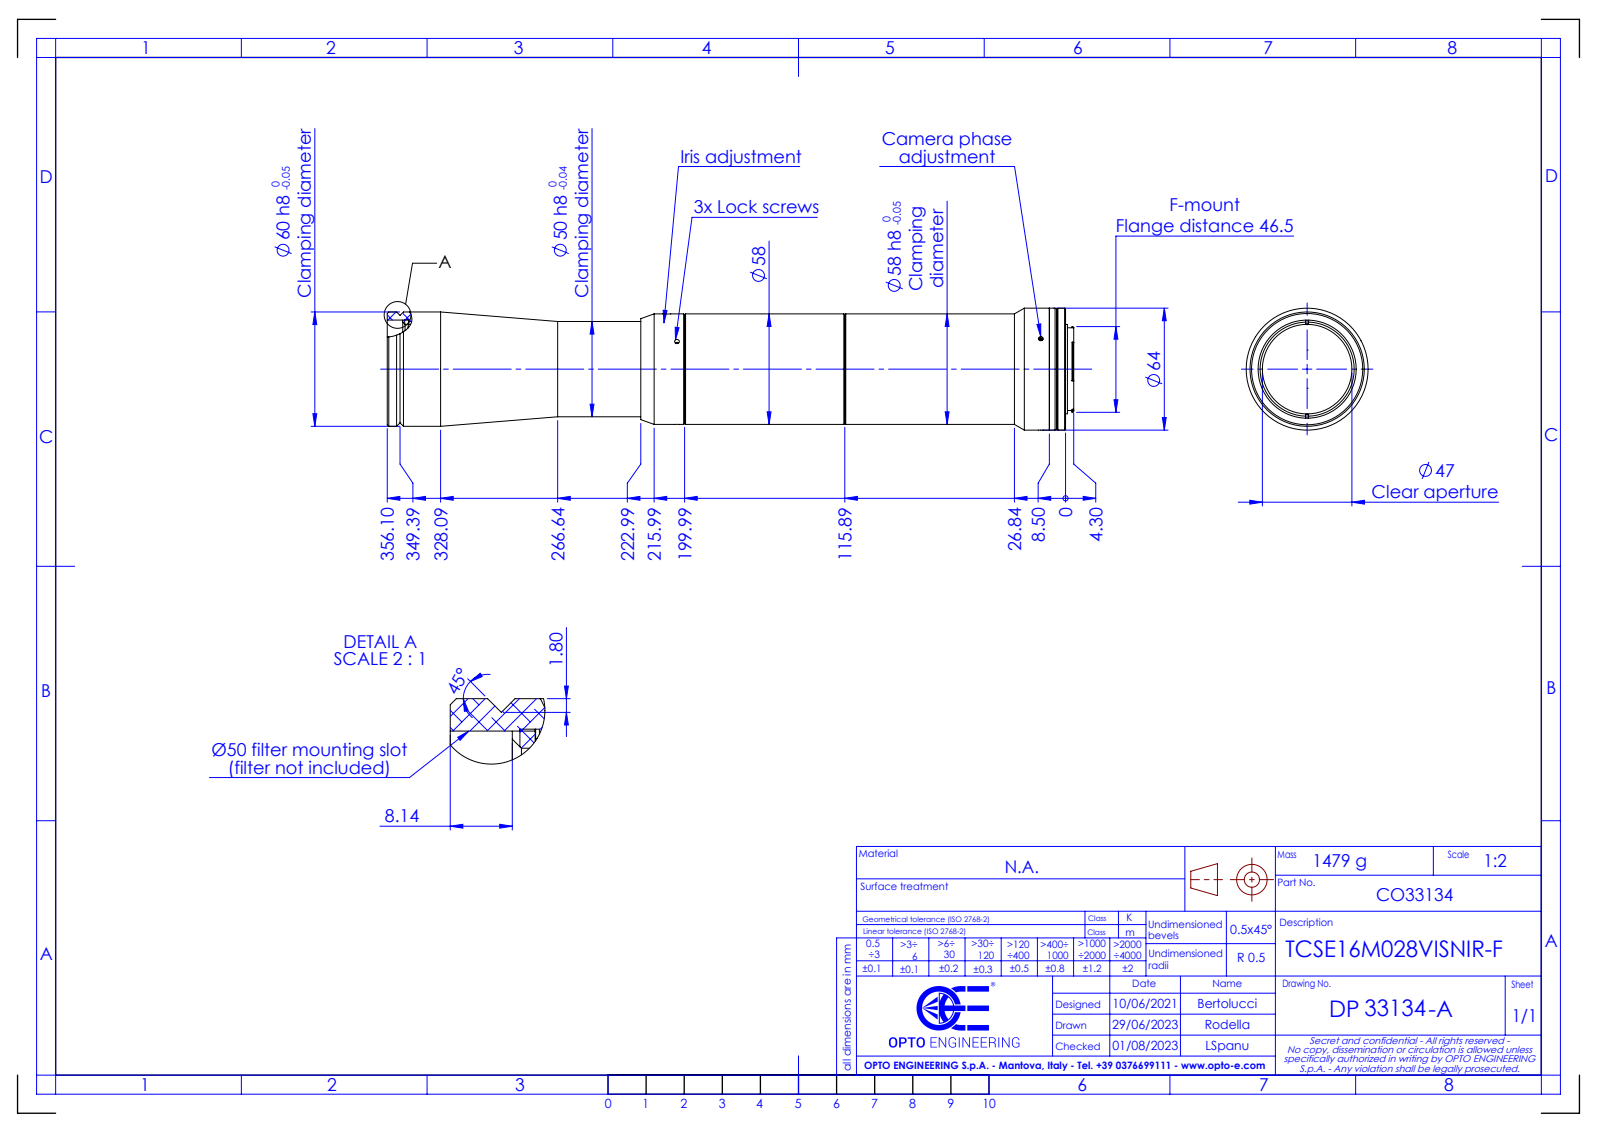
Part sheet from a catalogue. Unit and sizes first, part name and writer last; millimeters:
Units: millimetres
Overall size (bounding box): 360.4 × 64 × 64
Round holes (diameter × count): ⌀2.5 ×6, ⌀4.2 ×1, ⌀42 ×1, ⌀47 ×1, ⌀50 ×1, ⌀51.5 ×1
Round bosses / shafts (diameter × count): ⌀64 ×1, ⌀63.5 ×1, ⌀60 ×1, ⌀58 ×1, ⌀46.9 ×1, ⌀43.4 ×1
Partial cylindrical surfaces — rounded edges, fillets, slot ends (radius × count): R0.5 ×6, R1.15 ×2, R22.65 ×1
Main face-to-face distances: 115.89, 110.39, 5.5, 1.5, 111.89, 4, 107.39, 3, 4.5, 8.5
Hole centre spacings: 190.99, 5.35, 196.34
Bodies: 0 solids, 143 faces (42 planar, 61 cylindrical, 40 other)
Part name (STEP PRODUCT): DP33134-A_TCSE16M028VISNIR-F
STEP written by: SolidWorks 2021 (CONFIG_CONTROL_DESIGN)
